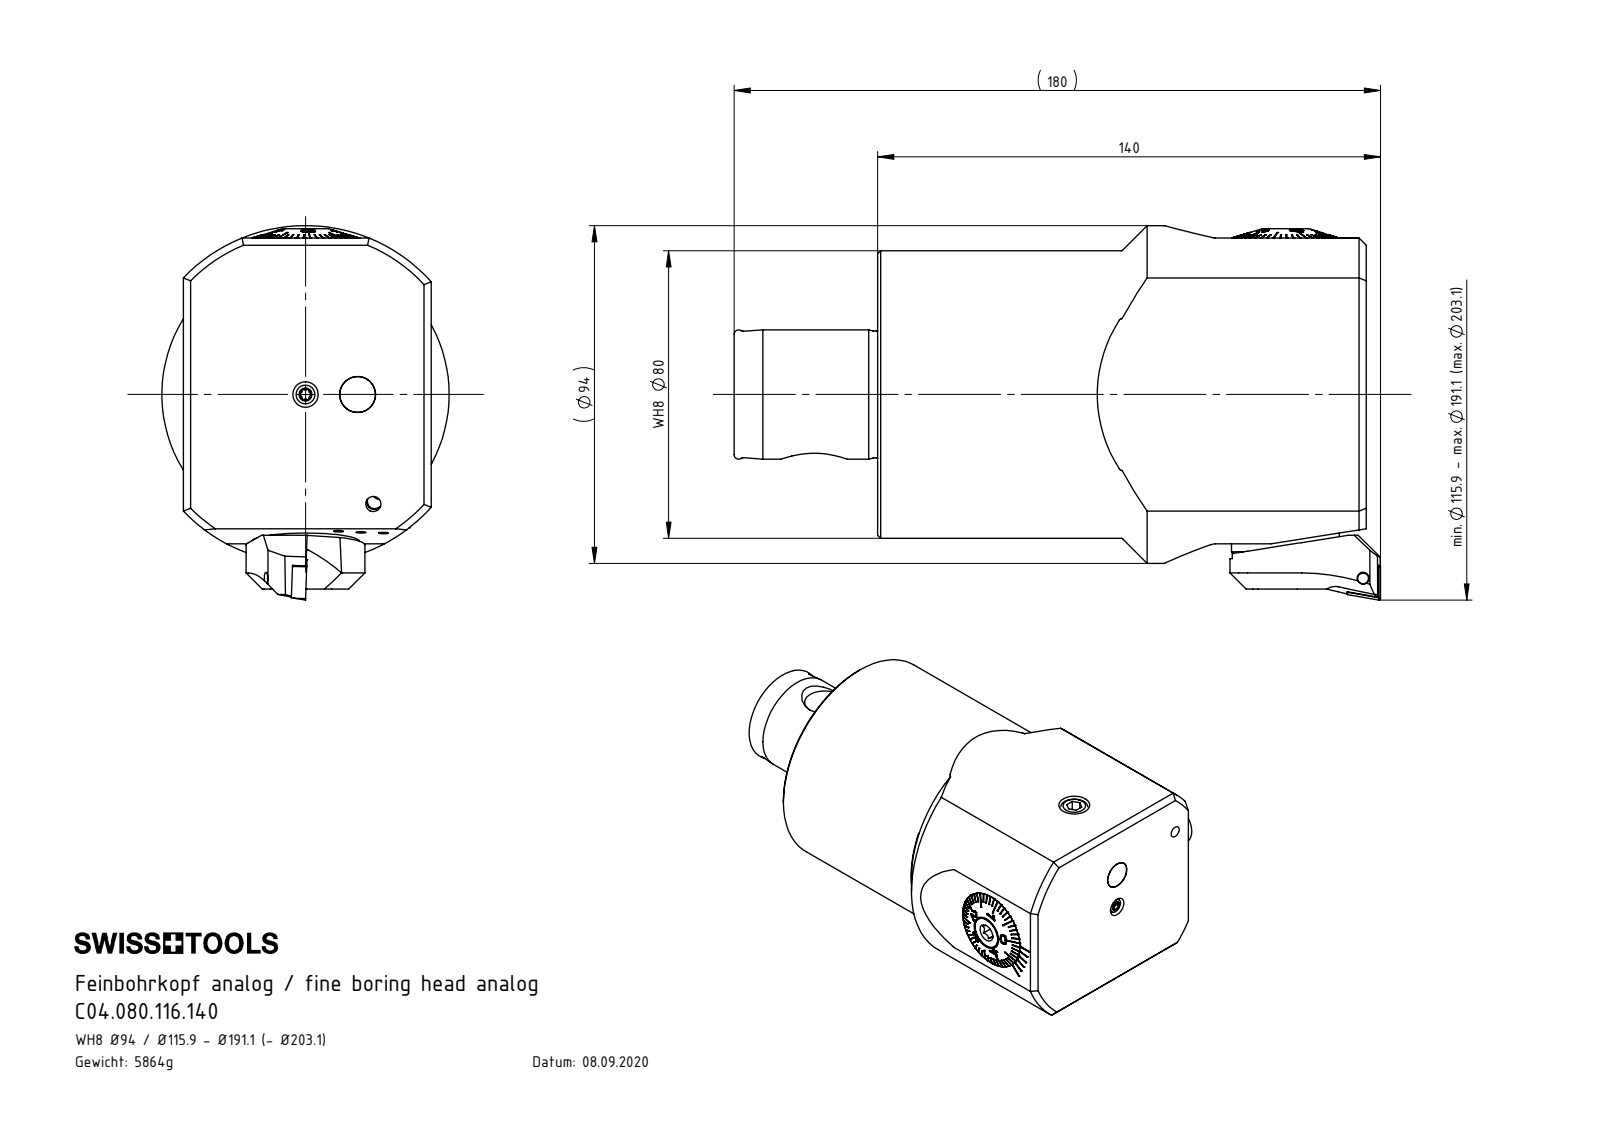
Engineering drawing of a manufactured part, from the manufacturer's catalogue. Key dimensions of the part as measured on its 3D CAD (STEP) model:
Part name (STEP PRODUCT): ISO 4026 - M10 x 16; C04.080.116.140; A55-BG3.011.033_A_gekrzt; Klebstoff D10 (+8 more)
STEP written by: SolidWorks 2017 (CONFIG_CONTROL_DESIGN)
Units: millimetres
Bodies: 14 solids, 732 faces (303 planar, 139 cylindrical, 290 other)
Overall size (bounding box): 176 × 101.15 × 80
Volume: 741 650 mm³ · Surface area: 87 572 mm²
Round holes (diameter × count): ⌀2.5 ×3, ⌀4.2 ×3, ⌀3.3 ×2, ⌀8.5 ×2, ⌀5 ×1, ⌀8 ×1, ⌀10 ×1, ⌀10.2 ×1, ⌀11.4 ×1, ⌀12 ×1, ⌀12.4 ×1, ⌀13 ×1
Round bosses / shafts (diameter × count): ⌀10 ×2, ⌀80 ×1, ⌀36 ×1, ⌀35.3 ×1, ⌀30 ×1, ⌀29.98 ×1, ⌀29.9 ×1, ⌀25 ×1
Partial cylindrical surfaces — rounded edges, fillets, slot ends (radius × count): R0.34 ×6, R0.59 ×6, R2.5 ×6, R2 ×4, R3.2 ×3, R0.5 ×2, R0.8 ×2, R1 ×1
Main face-to-face distances: 69, 136, 6.5, 40, 176, 78.6, 85.1, 2.6, 87.7, 2.5
Hole centre spacings: 14.5
